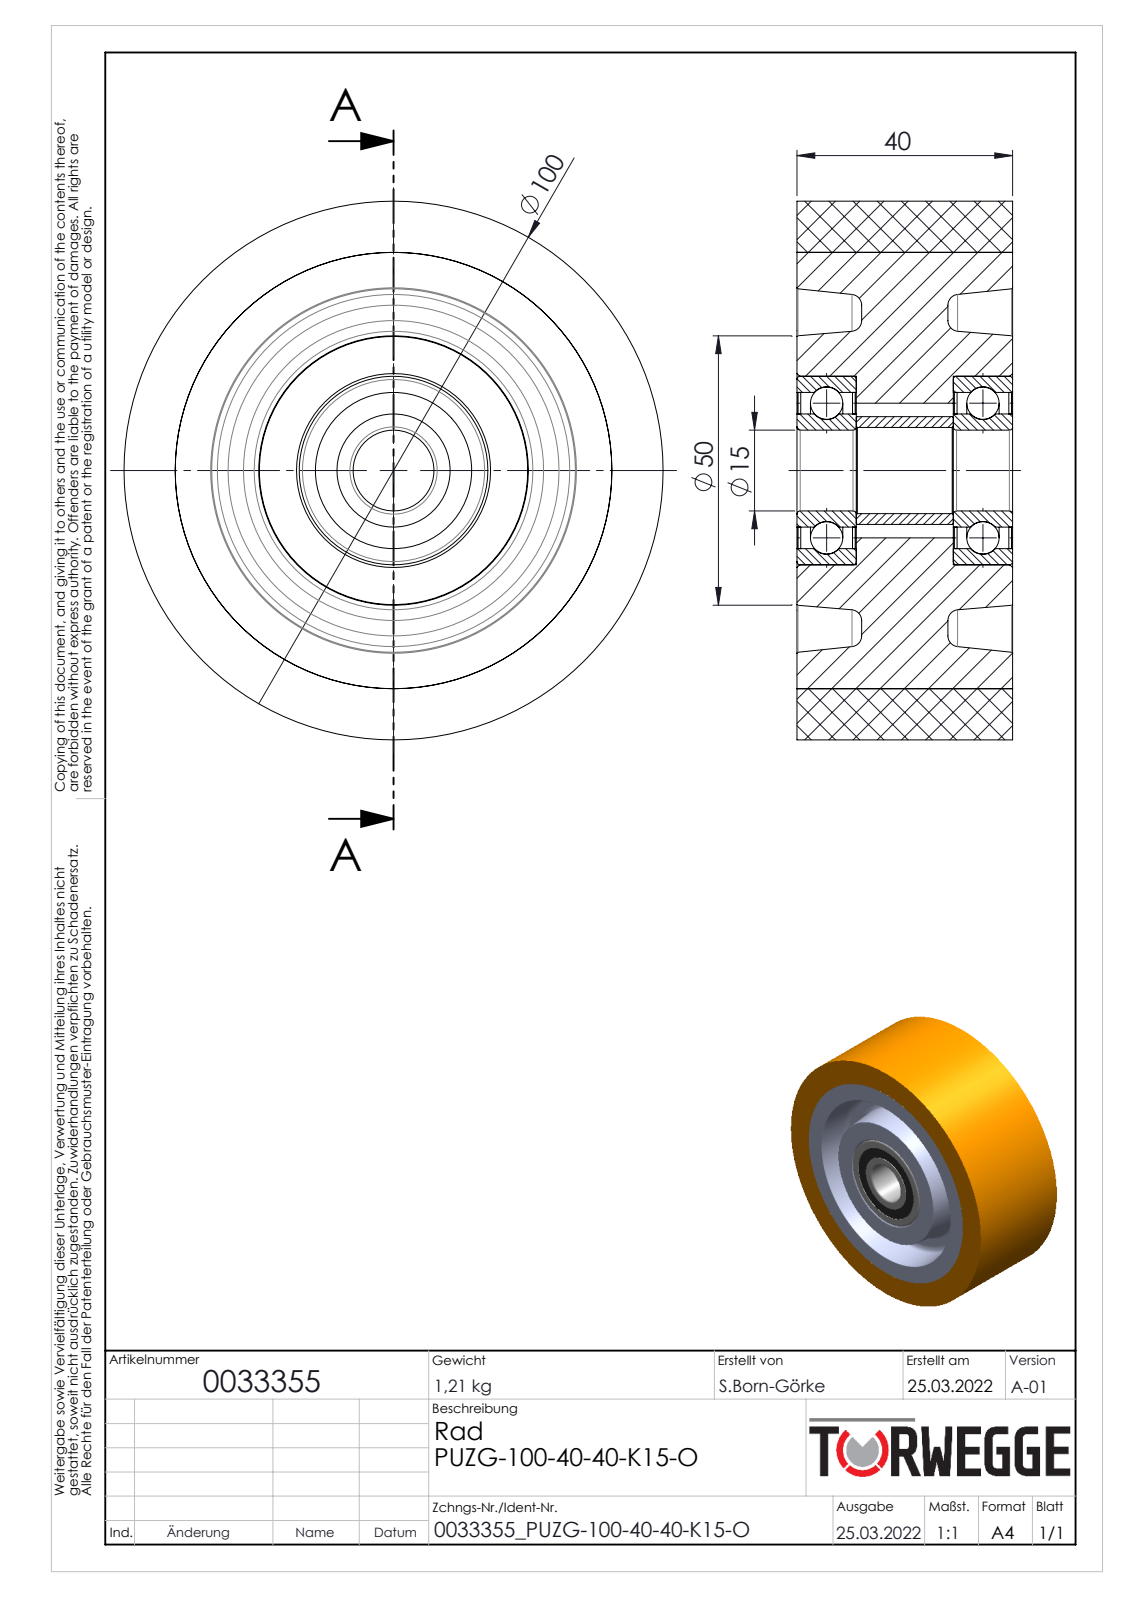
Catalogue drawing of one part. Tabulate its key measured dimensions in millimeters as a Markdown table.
| quantity | value |
| --- | --- |
| part name | 0033355 |
| STEP written by | SolidWorks 2020 (AUTOMOTIVE_DESIGN) |
| units | millimeters |
| bodies | 13 solids, 156 faces (28 planar, 56 cylindrical, 72 other) |
| overall size | 100 × 100 × 40 |
| volume | 267 288 mm³ |
| surface area | 75 760 mm² |
| round holes (diameter × count) | 15 × 1, 16 × 1, 21 × 1, 25 × 1, 29 × 1, 35 × 1, 81 × 1 |
| round bosses / shafts (diameter × count) | 100 × 1, 20 × 1 |
| main face-to-face distances | 40, 29, 11, 0.7, 10.3, 10.8, 0.5, 10.1, 12, 28 |
